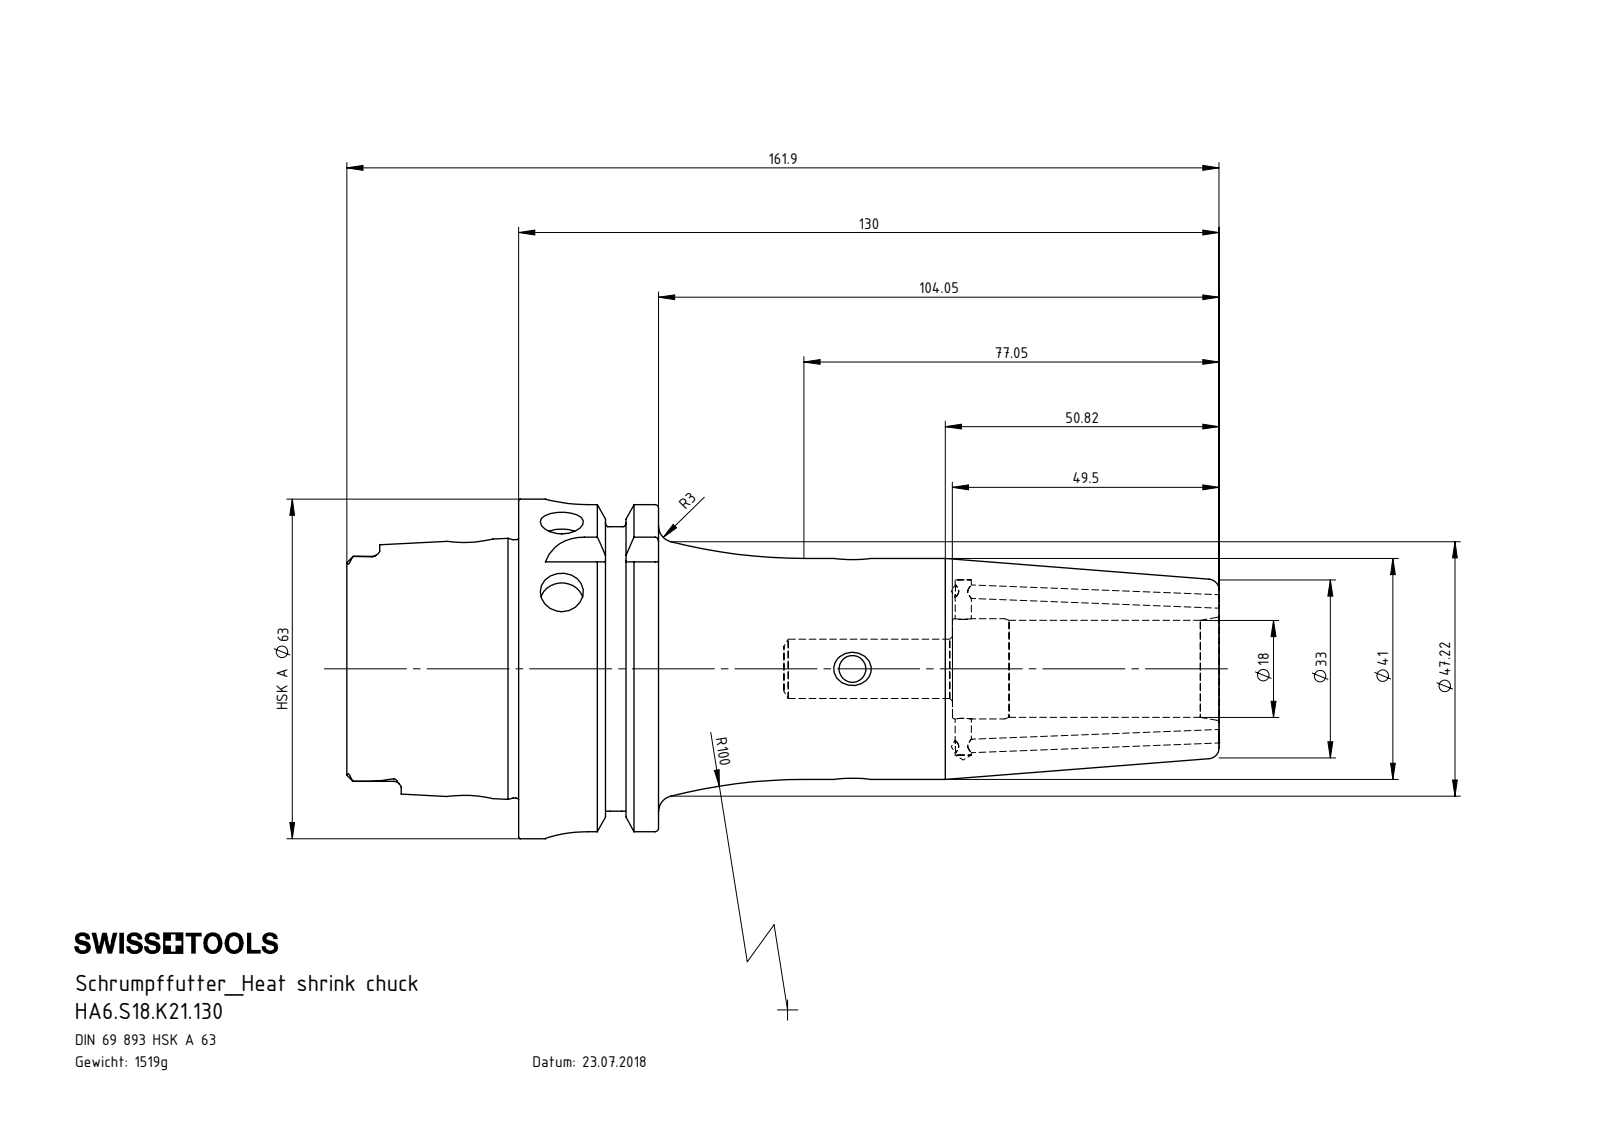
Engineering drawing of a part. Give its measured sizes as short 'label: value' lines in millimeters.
name: HA6-S18.K21.130; ERU-AN5.K01.020_A; ERU-CJ2.001.006; HA6-S18.K21.130_C_Fertigbearbeitung
written by: SolidWorks 2012 (CONFIG_CONTROL_DESIGN)
unit: mm
bodies: 4 solids, 312 faces (102 planar, 85 cylindrical, 125 other)
size: 161.98 × 63 × 63
volume: 193 542 mm³; area: 41 771 mm²
holes: 2× ⌀2.5, 2× ⌀5, 2× ⌀8, 1× ⌀3, 1× ⌀6, 1× ⌀7.5, 1× ⌀8.4, 1× ⌀10, 1× ⌀11, 1× ⌀17, 1× ⌀18, 1× ⌀18.6
bosses: 2× ⌀3, 1× ⌀63, 1× ⌀54.95, 1× ⌀47.94, 1× ⌀41, 1× ⌀12
rounds: 6× R1.4, 4× R2.88, 4× R8
face distances: 25.95, 16, 9.95, 31.9, 41.85, 57.85, 161.9, 130, 120.05, 104.05
hole spacings: 20.55, 54.95, 70.95, 91.5
